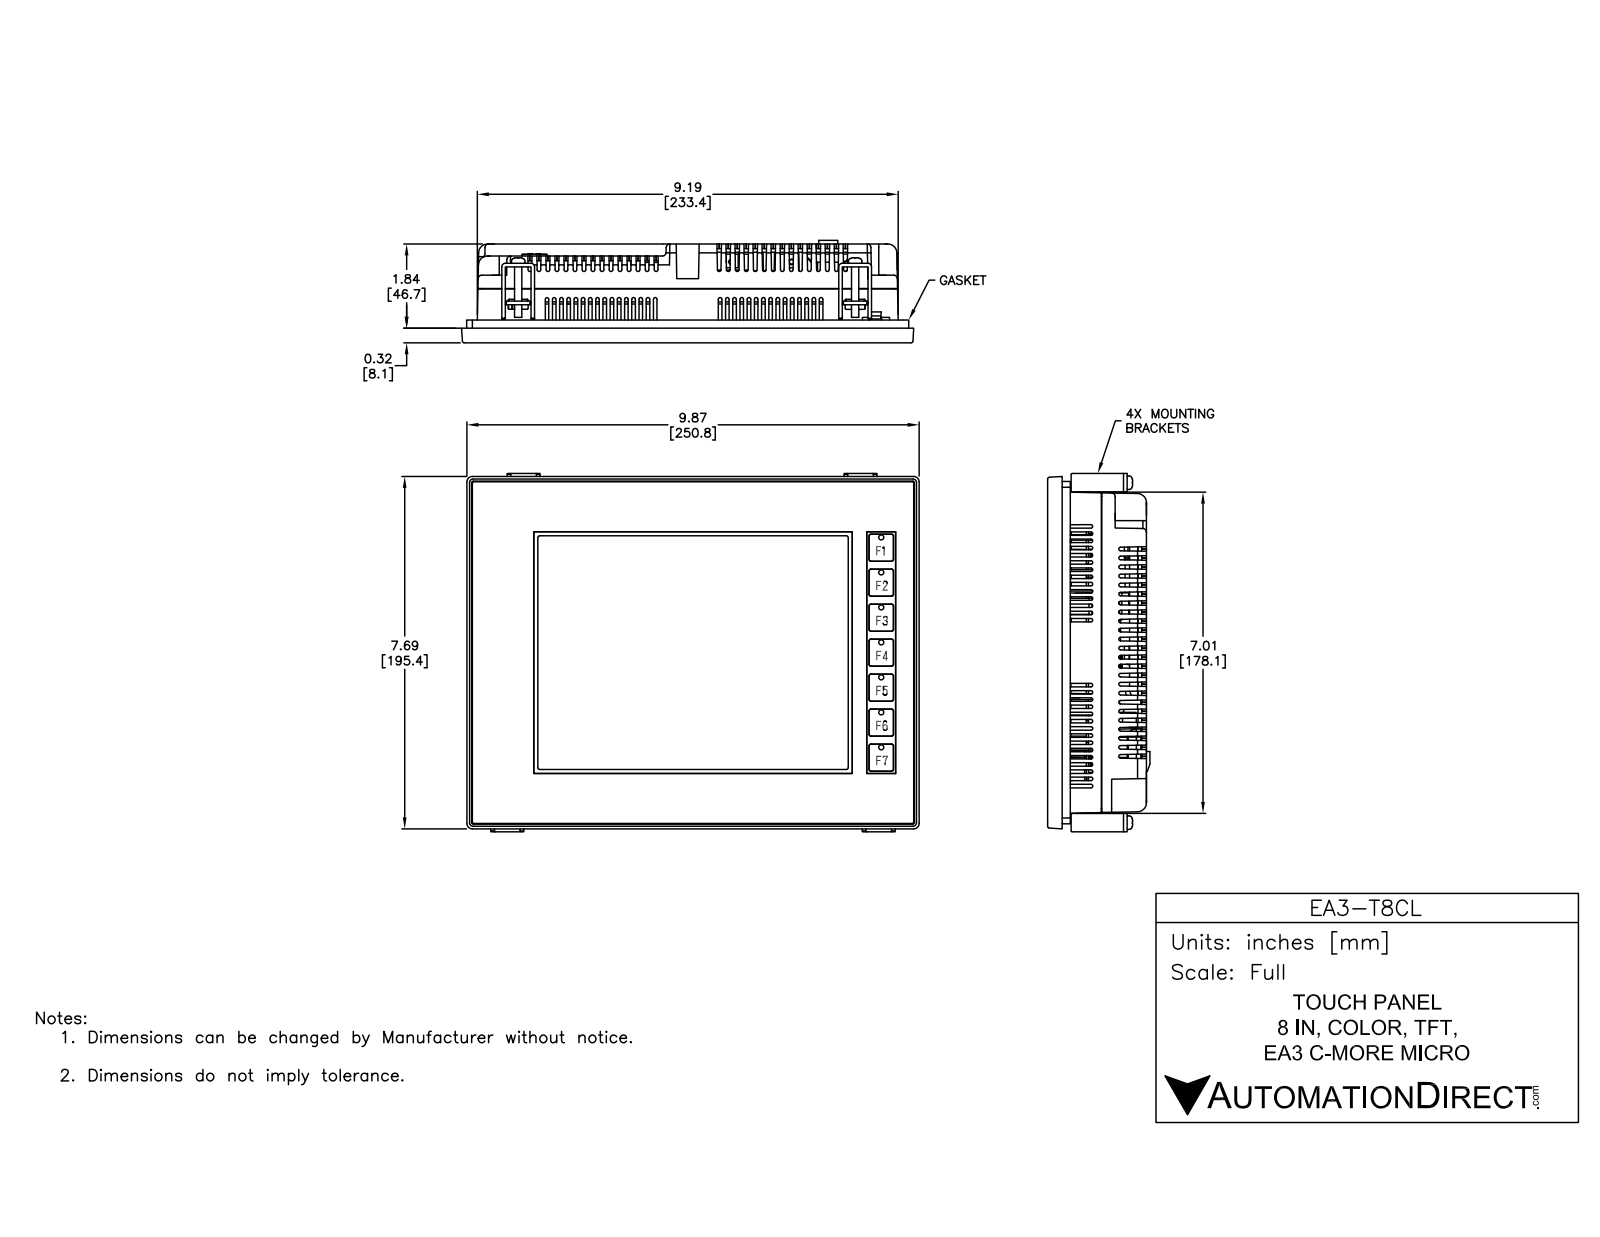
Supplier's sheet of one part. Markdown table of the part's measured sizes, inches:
| quantity | value |
| --- | --- |
| part name | EA3-T8CL_140124 |
| STEP written by | SolidWorks 2013 (CONFIG_CONTROL_DESIGN) |
| units | inches |
| bodies | 1 solid, 5602 faces (3820 planar, 1034 cylindrical, 748 other) |
| overall size | 9.874 × 7.823 × 2.236 |
| volume | 130.1 in³ |
| surface area | 309.1 in² |
| round holes (diameter × count) | 0.039 × 18, 0.11 × 10, 0.157 × 4, 0.098 × 2, 0.102 × 2, 0.12 × 2 |
| round bosses / shafts (diameter × count) | 0.248 × 7, 0.294 × 4, 0.098 × 3, 0.031 × 3 |
| partial cylindrical surfaces (radius × count) | 0.039 × 108, 0.047 × 108, 0.079 × 81, 0.043 × 62, 0.02 × 60, 0.031 × 28, 0.059 × 12, 0.008 × 9 |
| main face-to-face distances | 2.148, 1.885, 0.264, 0.197, 0.487, 1.398, 1.661, 1.575, 2.143, 1.656 |
| hole center spacings | 0.124, 0.109, 0.218, 0.327, 0.198, 0.198, 0.294, 0.436 |
